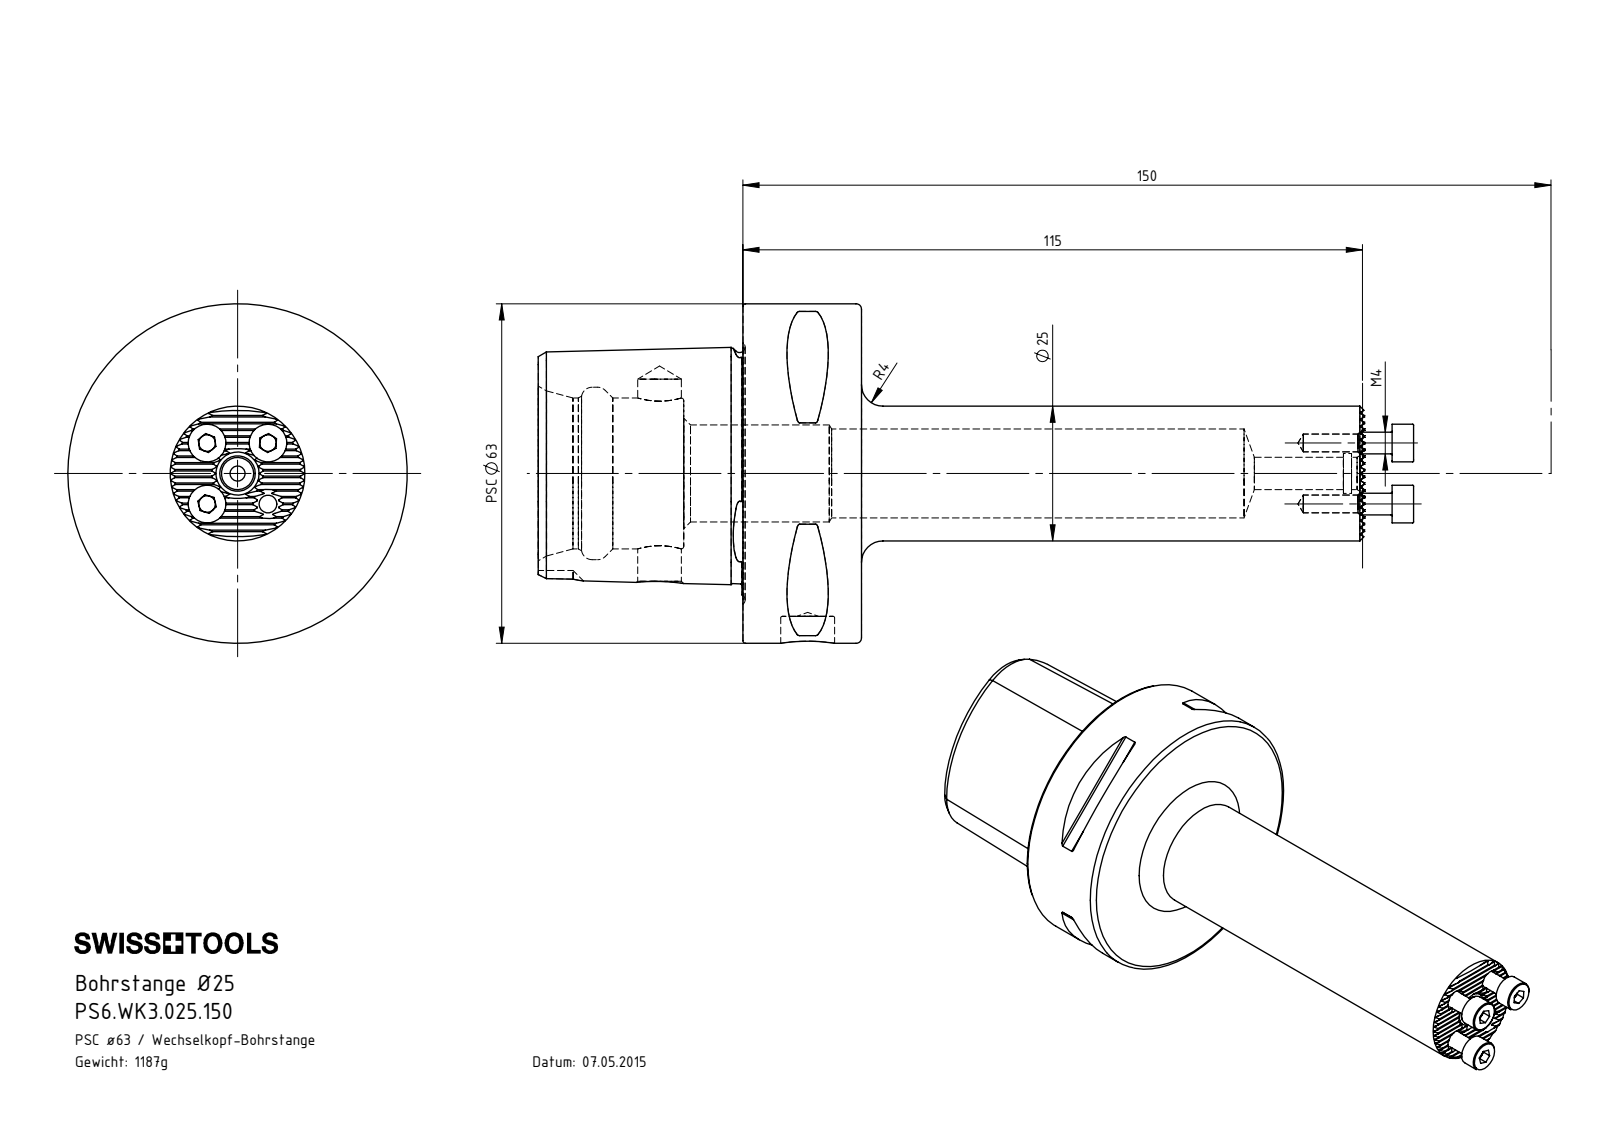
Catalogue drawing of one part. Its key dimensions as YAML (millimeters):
part_name: "DIN 3771 - 6x1; WK1-ER1.016.075_A_Fertigbearbeitung; WK1-ER1.016.002_A_Fertigbearbeitung; PS6-WK3.025.150_A (+2 more)"
step_written_by: "SolidWorks 2017 (AUTOMOTIVE_DESIGN)"
units: millimeters
bodies: {solids: 7, faces: 433, planar: 201, cylindrical: 103, other: 129}
overall_size: [162.5, 63, 63]
volume: 139979
surface_area: 38455
round_holes:
  - {diameter: 3.3, count: 4}
  - {diameter: 3, count: 1}
  - {diameter: 4, count: 1}
  - {diameter: 6, count: 1}
  - {diameter: 7.4, count: 1}
  - {diameter: 8.1, count: 1}
  - {diameter: 16.5, count: 1}
  - {diameter: 18, count: 1}
  - {diameter: 28, count: 1}
  - {diameter: 32, count: 1}
round_bosses_or_shafts:
  - {diameter: 7, count: 3}
  - {diameter: 4, count: 3}
  - {diameter: 63, count: 1}
  - {diameter: 25, count: 1}
  - {diameter: 16, count: 1}
partial_cylinders:
  - {radius: 0.12, count: 19}
  - {radius: 0.5, count: 8}
  - {radius: 6, count: 1}
face_to_face_distances: [22, 38, 60, 129.5, 91.5, 69.5, 33, 102.5, 24.88, 104]
hole_center_spacings: [8, 11.32, 16.01, 27.5]
